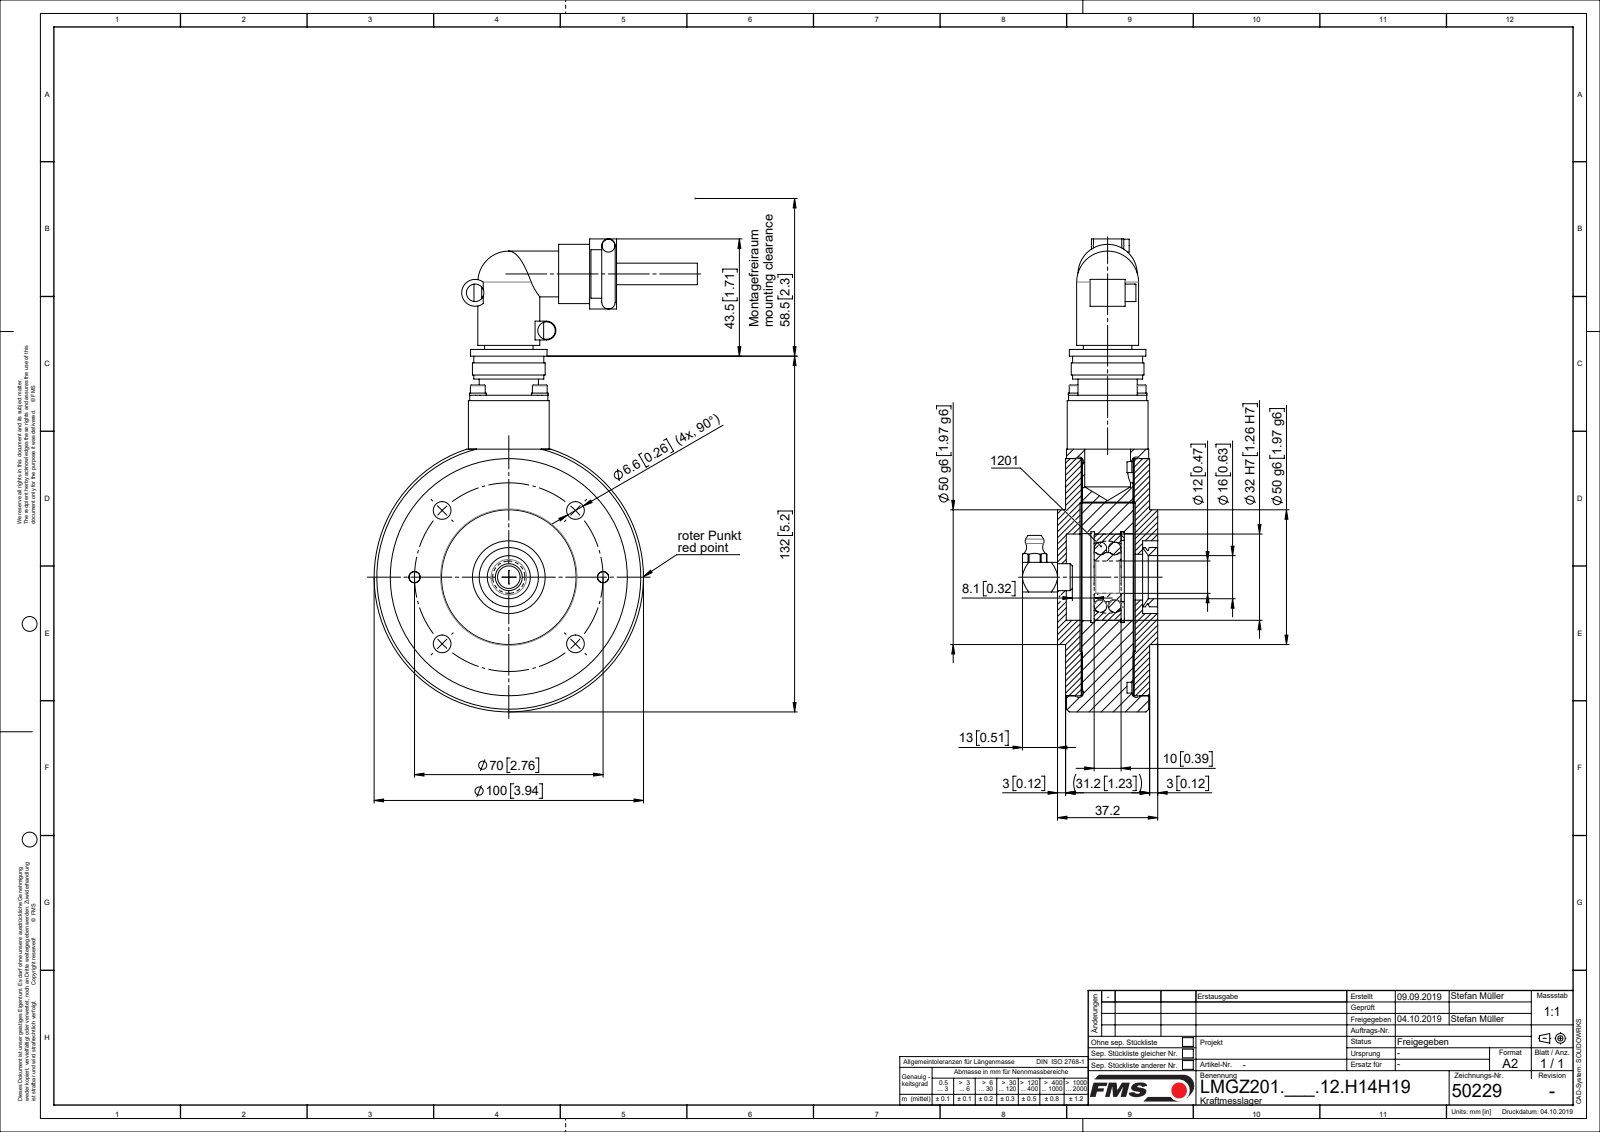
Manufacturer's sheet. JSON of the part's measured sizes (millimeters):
{"part_name": "ZEICHNUNG7; L50229; L4866604; TEIL1 (+8 more)", "step_written_by": "Mechanical Desktop 2007 (CONFIG_CONTROL_DESIGN)", "units": "millimeters", "bodies": {"solids": 21, "faces": 411, "planar": 133, "cylindrical": 227, "other": 51}, "overall_size": [175.5, 120, 51.7], "volume_mm3": 275901, "surface_area_mm2": 99653, "round_holes": [[2.6, 4], [3.2, 4], [3.4, 4], [3.5, 4], [6.6, 4], [4, 2], [5.5, 2], [10, 2], [8.68, 1], [12, 1], [16, 1], [17, 1]], "round_bosses_or_shafts": [[8, 4], [6.2, 4], [5.5, 4], [3, 4], [22, 3], [6.5, 2], [5, 2], [4.8, 2]], "partial_cylinders_radius": [[2.5, 2], [3.5, 1], [5, 1]], "face_to_face_distances": [19.25, 19, 5.85, 25.1, 6.1, 25.35, 19.5, 5.5, 24.75, 20], "hole_center_spacings": [35, 16.26, 23, 26.79, 49.5, 64.67, 70, 32.53]}
